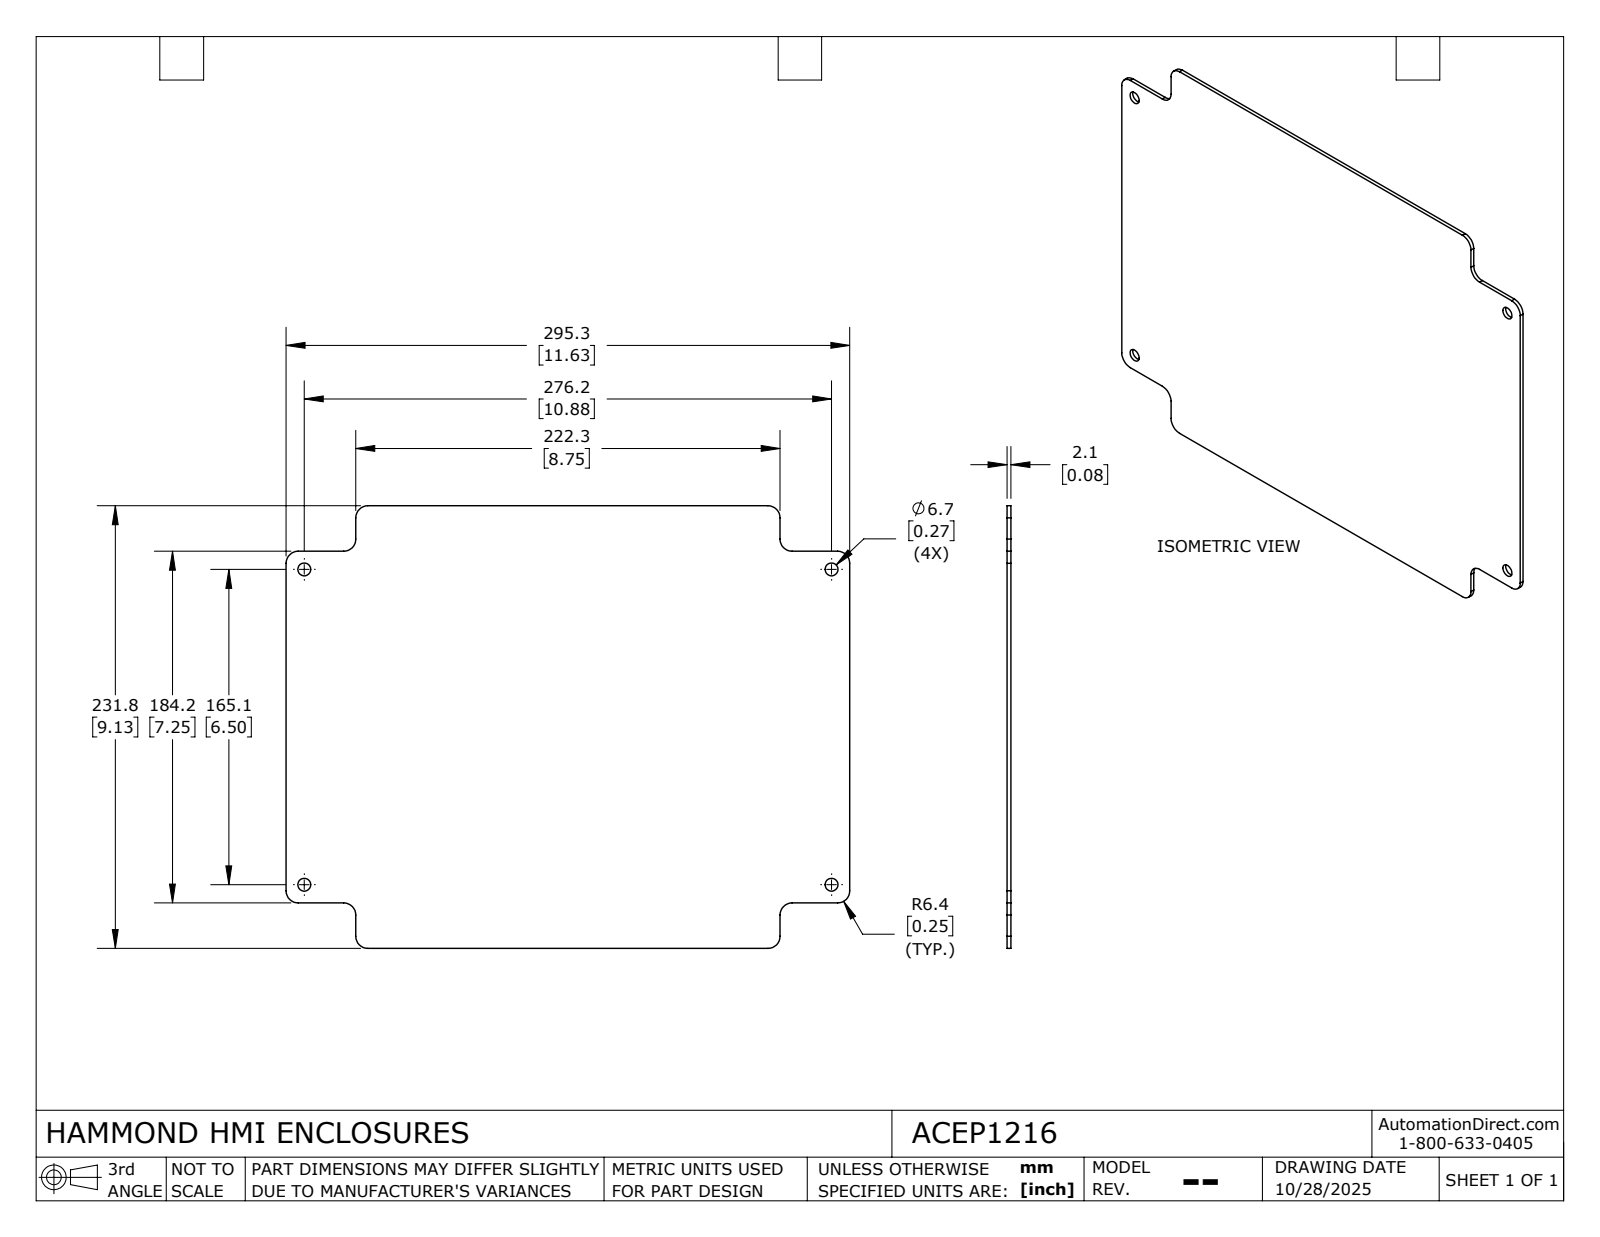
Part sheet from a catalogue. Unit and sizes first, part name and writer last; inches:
Units: inches
Overall size (bounding box): 11.625 × 9.125 × 0.081
Round holes (diameter × count): ⌀0.265 ×4
Partial cylindrical surfaces — rounded edges, fillets, slot ends (radius × count): R0.25 ×12
Main face-to-face distances: 0.081, 9.125, 11.625, 0.937, 8.188, 7.25, 1.438, 10.187, 8.75
Hole centre spacings: 6.5, 10.875, 12.669
Volume: 8.133 in³ · Surface area: 204.4 in²
Bodies: 1 solid, 30 faces (14 planar, 16 cylindrical, 0 other)
Part name (STEP PRODUCT): ACEP1216
STEP written by: SolidWorks 2024 (AUTOMOTIVE_DESIGN)
